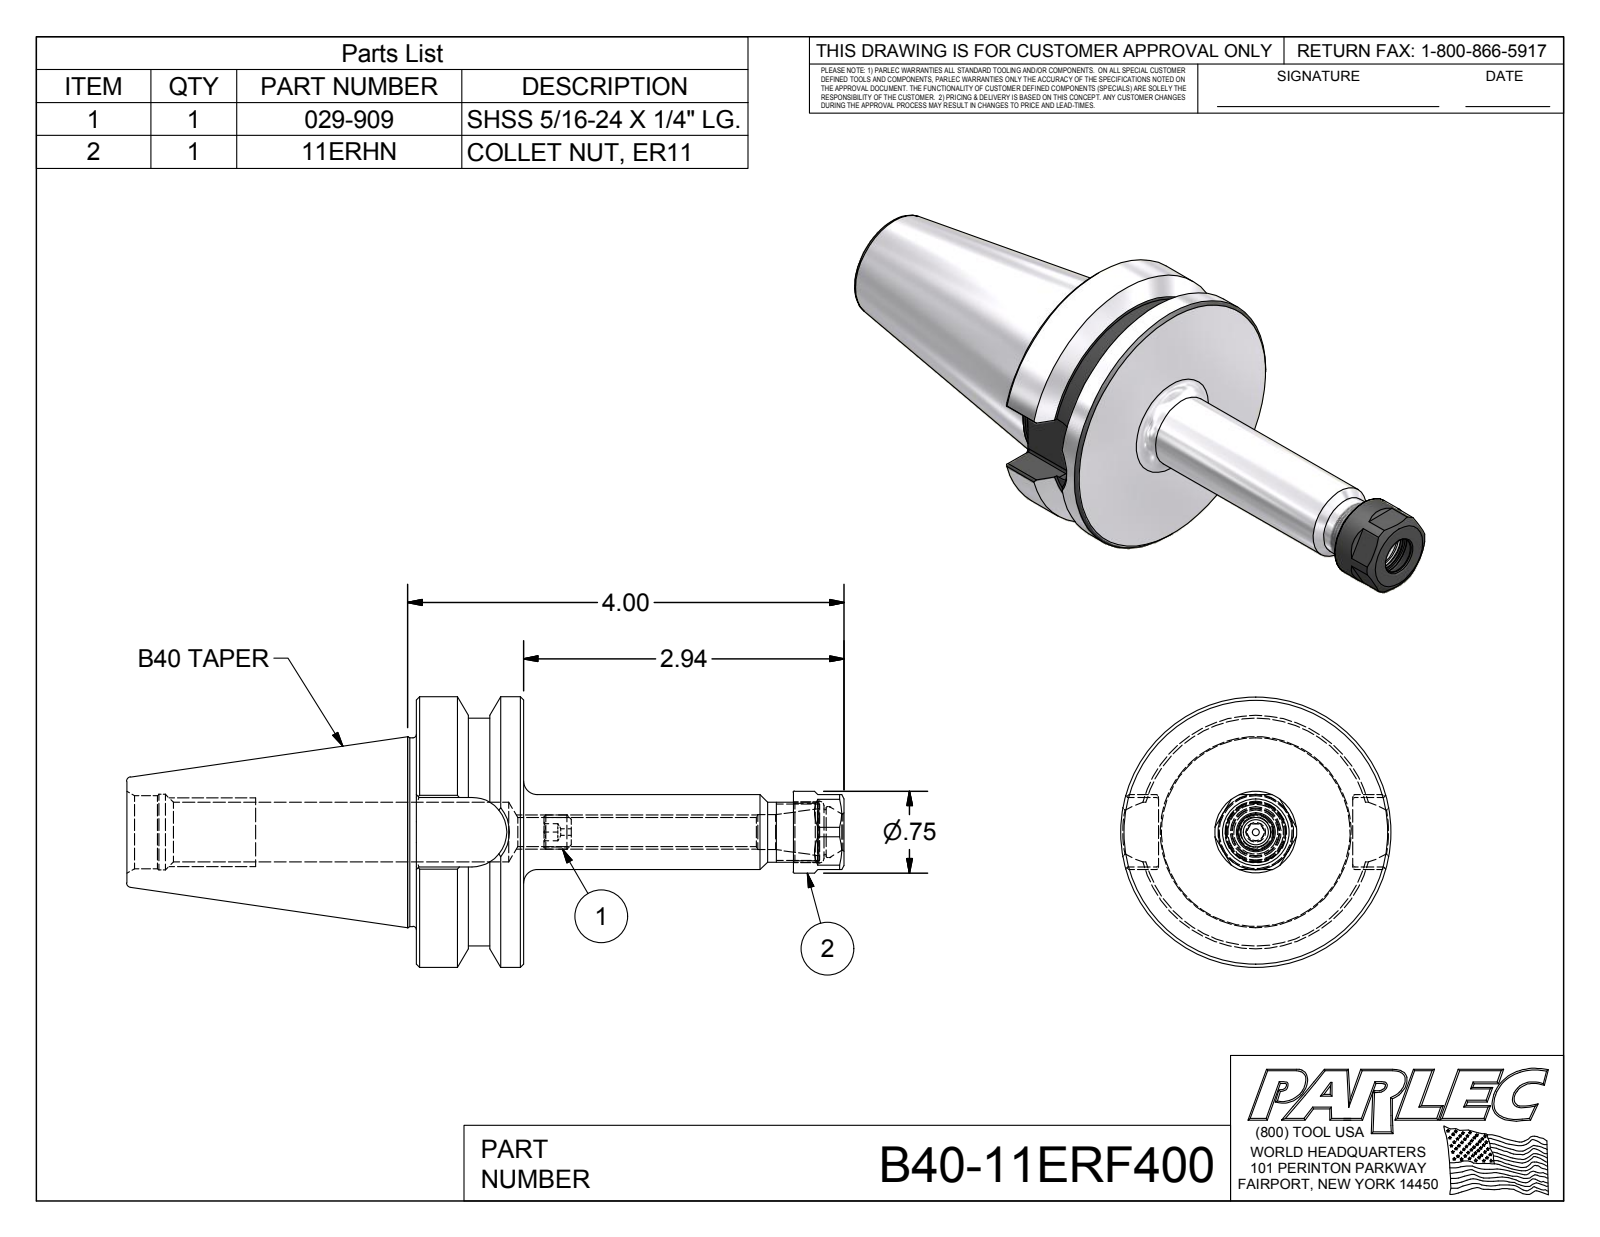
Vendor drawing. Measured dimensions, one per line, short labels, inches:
name: B40-11ERF400; 029-909; 11ERHN
written by: Autodesk Inventor 2012 (AUTOMOTIVE_DESIGN)
unit: in
bodies: 3 solids, 127 faces (53 planar, 30 cylindrical, 44 other)
size: 6.575 × 2.48 × 2.48
volume: 8.193 in³; area: 45.39 in²
holes: 1× ⌀0.06, 1× ⌀0.267, 1× ⌀0.32, 1× ⌀0.335, 1× ⌀0.465, 1× ⌀0.525, 1× ⌀0.545, 1× ⌀0.565, 1× ⌀0.67, 1× ⌀0.694
bosses: 1× ⌀2.48, 1× ⌀2.087, 1× ⌀1.73, 1× ⌀0.75, 1× ⌀0.688, 1× ⌀0.551, 1× ⌀0.313
rounds: 8× R0.02, 1× R0.319
face distances: 0.984, 1.78, 2.653, 3.637, 0.637, 6.575, 3.922, 2.938, 0.688, 6.11
